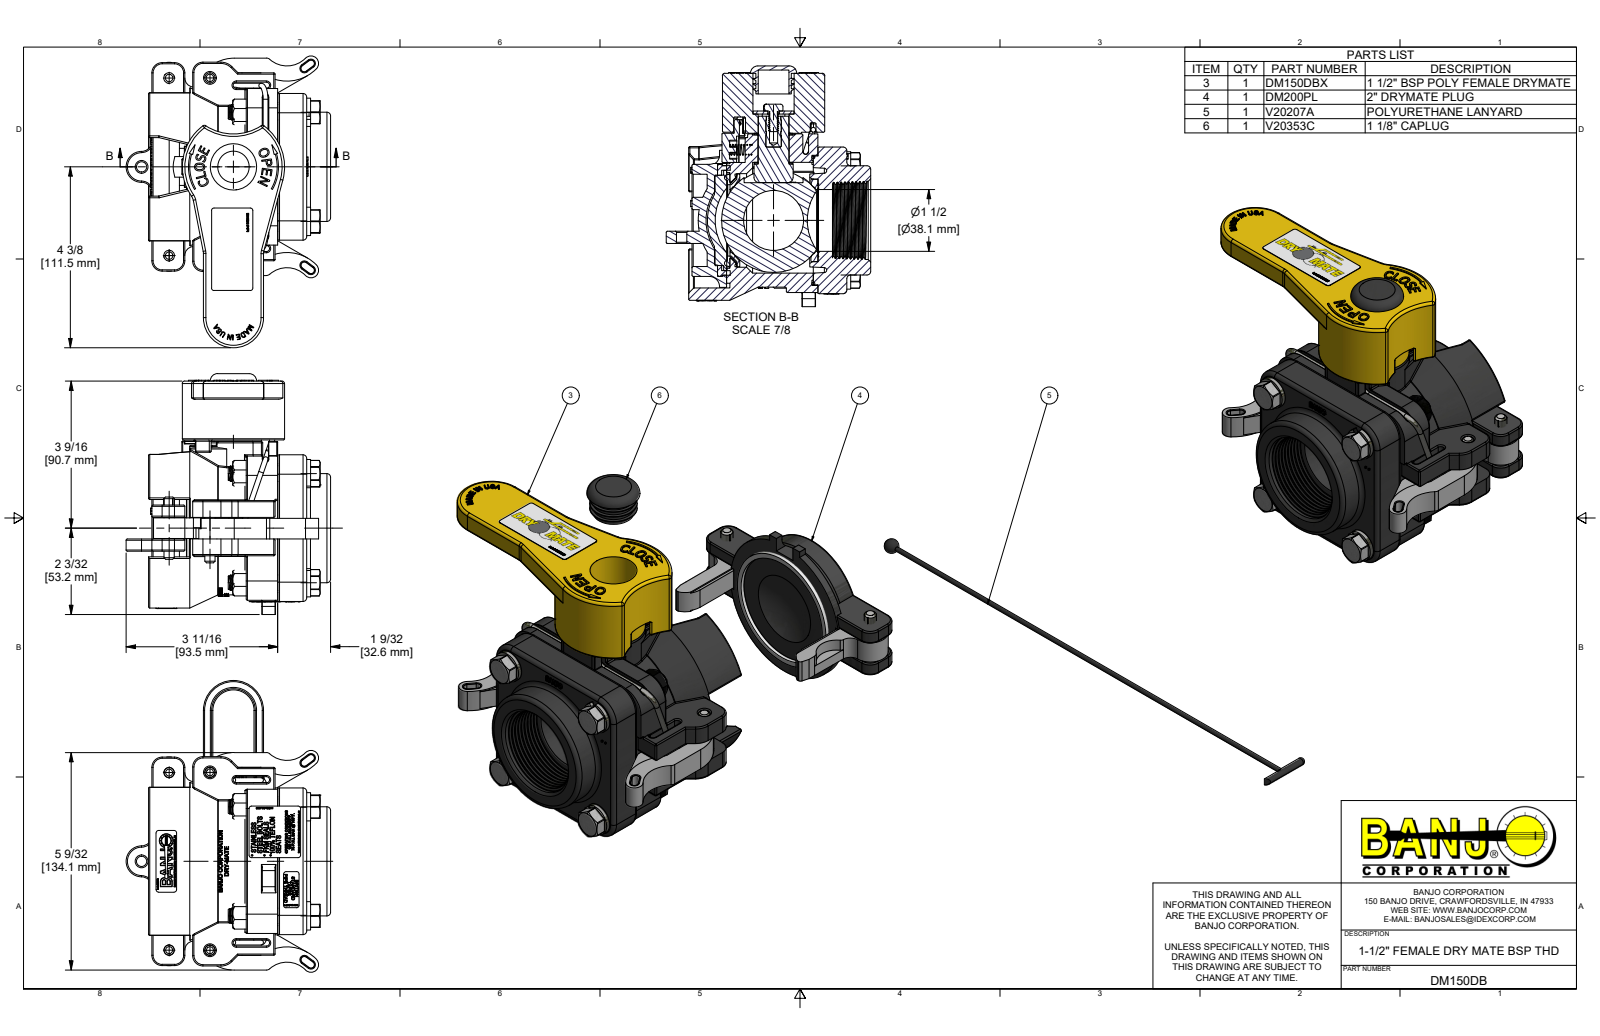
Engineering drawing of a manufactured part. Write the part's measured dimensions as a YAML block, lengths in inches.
part_name: "DM150DB; DM150DBX; DM20254F; DM20254FY (+8 more)"
step_written_by: "Autodesk Inventor 2022 (AUTOMOTIVE_DESIGN)"
units: inches
bodies: {solids: 45, faces: 7192, planar: 3452, cylindrical: 1049, other: 2691}
overall_size: [7.084, 5.845, 4.967]
volume: 46.16
surface_area: 400.1
round_holes:
  - {diameter: 0.25, count: 5}
  - {diameter: 0.375, count: 5}
  - {diameter: 0.256, count: 4}
  - {diameter: 0.307, count: 4}
  - {diameter: 0.385, count: 4}
  - {diameter: 0.406, count: 4}
  - {diameter: 0.41, count: 4}
  - {diameter: 0.125, count: 3}
  - {diameter: 0.196, count: 1}
  - {diameter: 0.2, count: 1}
  - {diameter: 0.227, count: 1}
  - {diameter: 0.281, count: 1}
round_bosses_or_shafts:
  - {diameter: 0.324, count: 60}
  - {diameter: 0.12, count: 5}
  - {diameter: 0.687, count: 4}
  - {diameter: 0.375, count: 4}
  - {diameter: 0.26, count: 4}
  - {diameter: 0.249, count: 4}
  - {diameter: 0.28, count: 3}
  - {diameter: 3.25, count: 1}
partial_cylinders:
  - {radius: 0.03, count: 159}
  - {radius: 0.01, count: 41}
  - {radius: 0.06, count: 39}
  - {radius: 0.02, count: 20}
  - {radius: 0.25, count: 11}
  - {radius: 0.12, count: 10}
  - {radius: 0.08, count: 8}
  - {radius: 0.09, count: 8}
face_to_face_distances: [0.11, 0.92, 2.217, 0.298, 0.013, 2.922, 0.5, 0.08, 0.7, 1.517]
hole_center_spacings: [2.654, 1.872, 1.881, 2.648, 2.66, 3.753, 0.95, 0.992]
